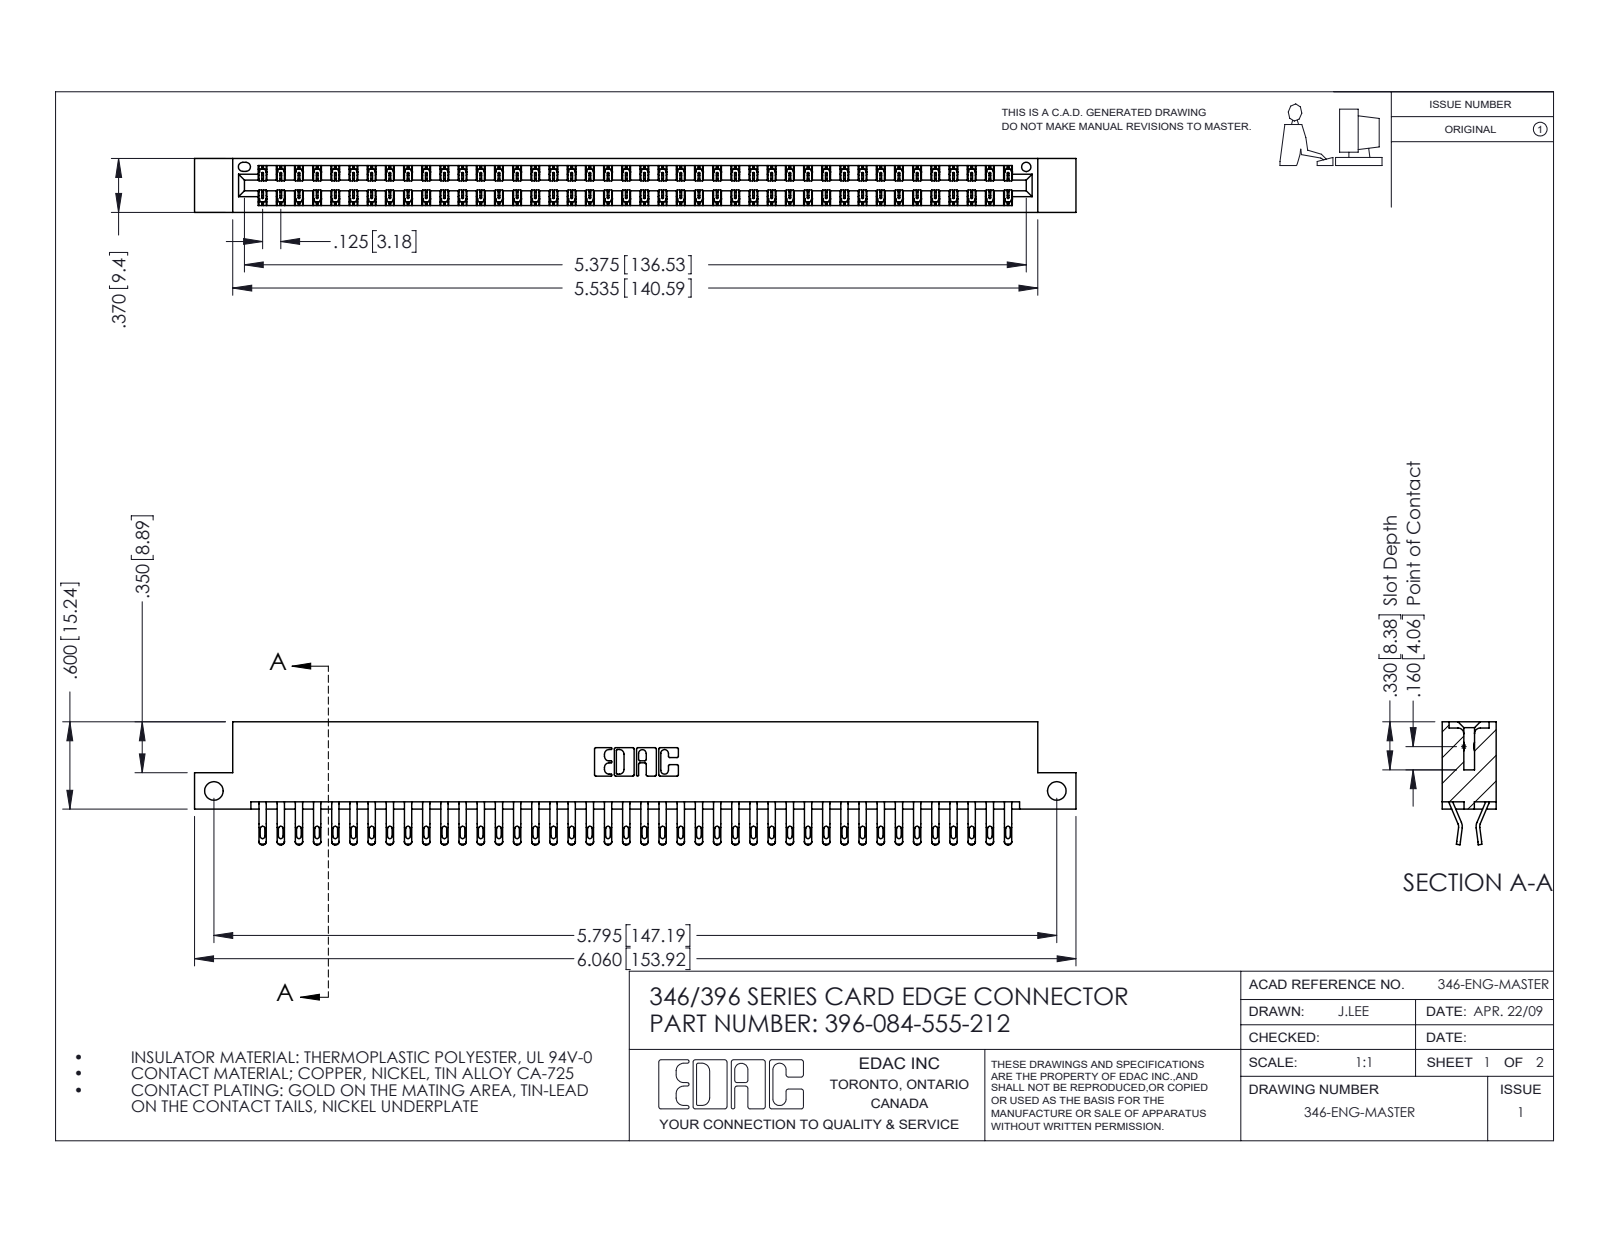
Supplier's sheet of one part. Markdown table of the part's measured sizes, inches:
| quantity | value |
| --- | --- |
| part name | 345-292-001_555 Tail; 346 Part_Flush Mounting Lugs - Side Mount; 396-084-555-212 |
| STEP written by | SolidWorks 2016 (CONFIG_CONTROL_DESIGN) |
| units | inches |
| bodies | 85 solids, 4994 faces (2848 planar, 2146 cylindrical, 0 other) |
| overall size | 6.06 × 0.845 × 0.37 |
| volume | 0.925 in³ |
| surface area | 33.45 in² |
| round holes (diameter × count) | 0.128 × 2, 0.064 × 1 |
| partial cylindrical surfaces (radius × count) | 0.016 × 168, 0.02 × 168, 0.006 × 126, 0.01 × 22, 0.007 × 6, 0.031 × 6, 0.026 × 3, 0.01 × 2 |
| main face-to-face distances | 0.048, 0.322, 0.37, 0.25, 0.025, 0.072, 0.298, 0.275, 0.148, 0.222 |
| hole center spacings | 5.795 |
